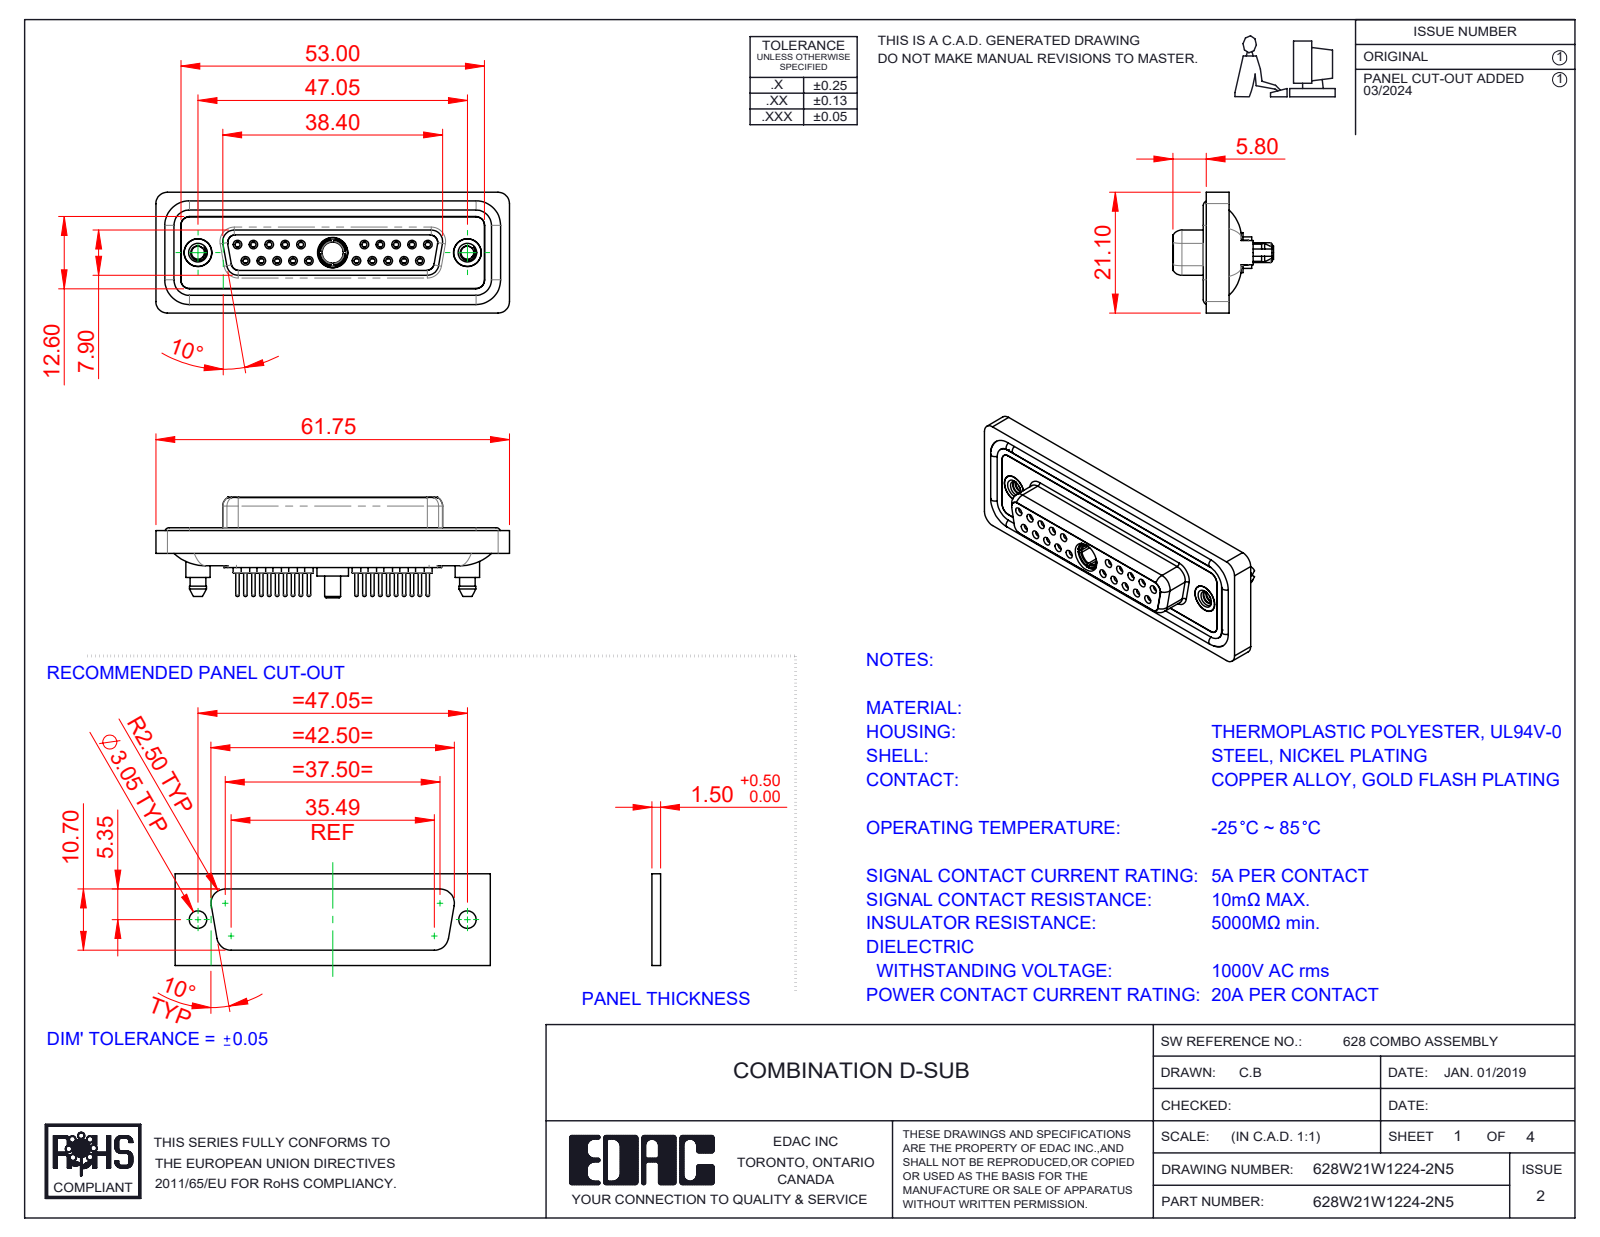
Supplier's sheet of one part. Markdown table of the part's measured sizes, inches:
| quantity | value |
| --- | --- |
| part name | 628Combo Threaded Boardlock_5; 628Combo Shell Front_25 Contacts; 628Combo Housing_21W1; 628Combo Contact Row 1_24 (+5 more) |
| STEP written by | SolidWorks 2023 (CONFIG_CONTROL_DESIGN) |
| units | inches |
| bodies | 29 solids, 1610 faces (450 planar, 623 cylindrical, 537 other) |
| overall size | 2.431 × 0.831 × 0.691 |
| volume | 0.519 in³ |
| surface area | 22.22 in² |
| round holes (diameter × count) | 0.035 × 20, 0.043 × 20, 0.059 × 20, 0.079 × 20, 0.063 × 10, 0.067 × 10, 0.191 × 3, 0.089 × 2, 0.157 × 2, 0.159 × 2, 0.197 × 2, 0.146 × 1 |
| round bosses / shafts (diameter × count) | 0.087 × 20, 0.024 × 20, 0.063 × 14, 0.213 × 2, 0.195 × 2, 0.189 × 2, 0.167 × 2, 0.217 × 1 |
| partial cylindrical surfaces (radius × count) | 0.059 × 24, 0.079 × 18, 0.063 × 10, 0.053 × 8, 0.01 × 4, 0.02 × 4, 0.024 × 4, 0.026 × 4 |
| main face-to-face distances | 0.016, 0.071, 0.293, 0.26, 0.222, 0.063, 0.02, 0.278, 0.114, 0.043 |
| hole center spacings | 0.124, 0.109, 0.218, 0.198, 0.327, 0.294, 0.654, 0.763 |
